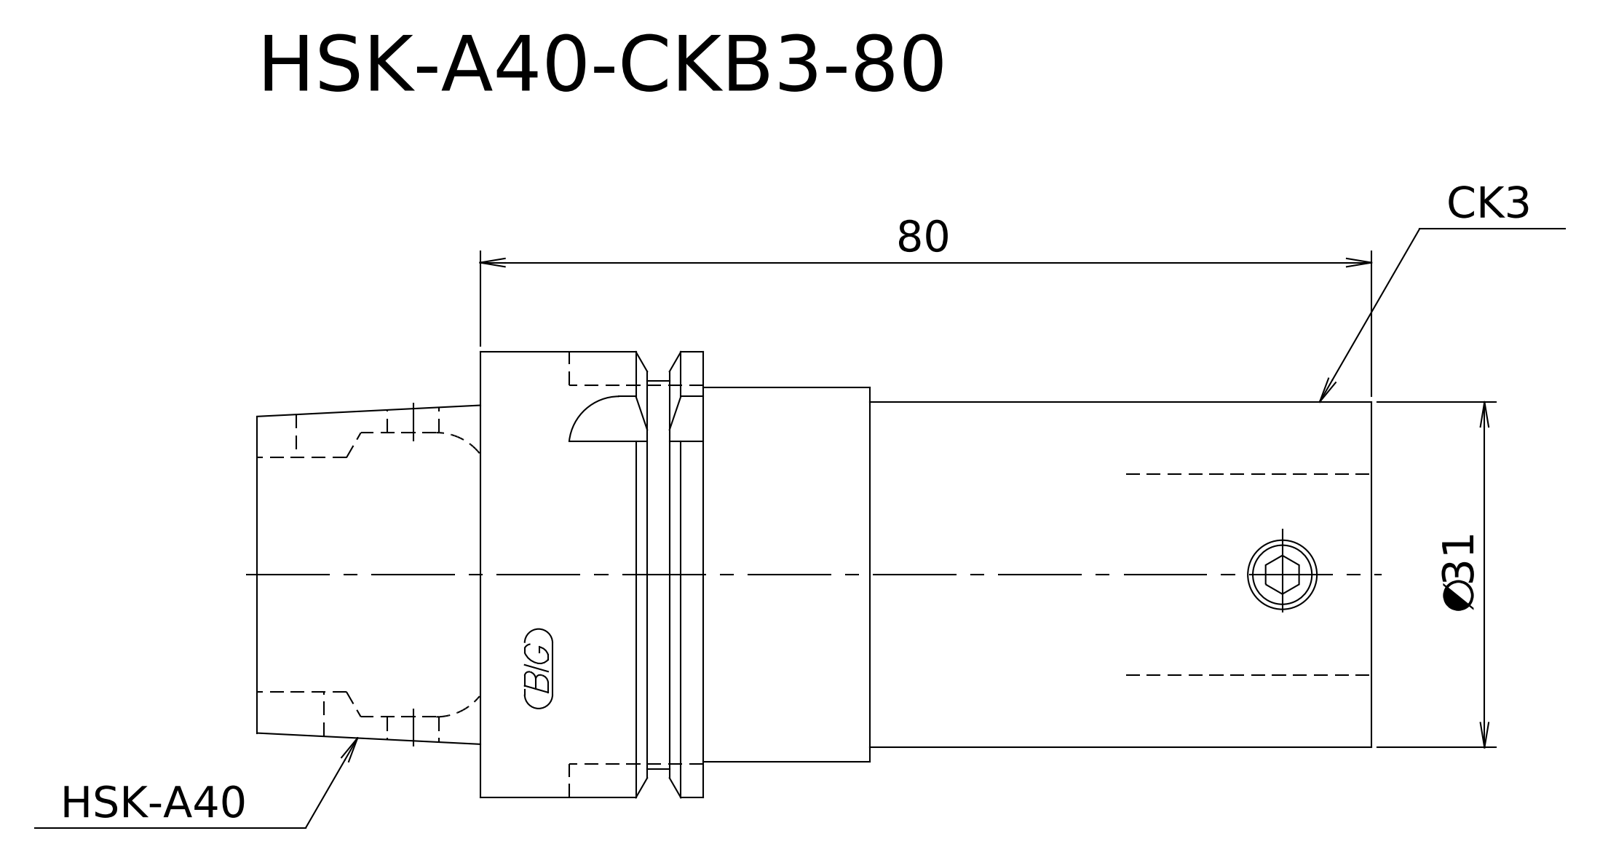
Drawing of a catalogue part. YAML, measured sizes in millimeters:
step_written_by: "Kubotek KeyCreator V8.5.1 (14335) (CONFIG_CONTROL_DESIGN)"
units: millimeters
bodies: {solids: 1, faces: 16, planar: 7, cylindrical: 6, other: 3}
overall_size: [100, 40, 40]
volume: 85144
surface_area: 13144
round_bosses_or_shafts:
  - {diameter: 40, count: 1}
  - {diameter: 34.8, count: 1}
  - {diameter: 33.6, count: 1}
  - {diameter: 31, count: 1}
  - {diameter: 30.25, count: 1}
face_to_face_distances: [20, 100, 80, 60, 40, 15, 35, 45, 55, 63]
